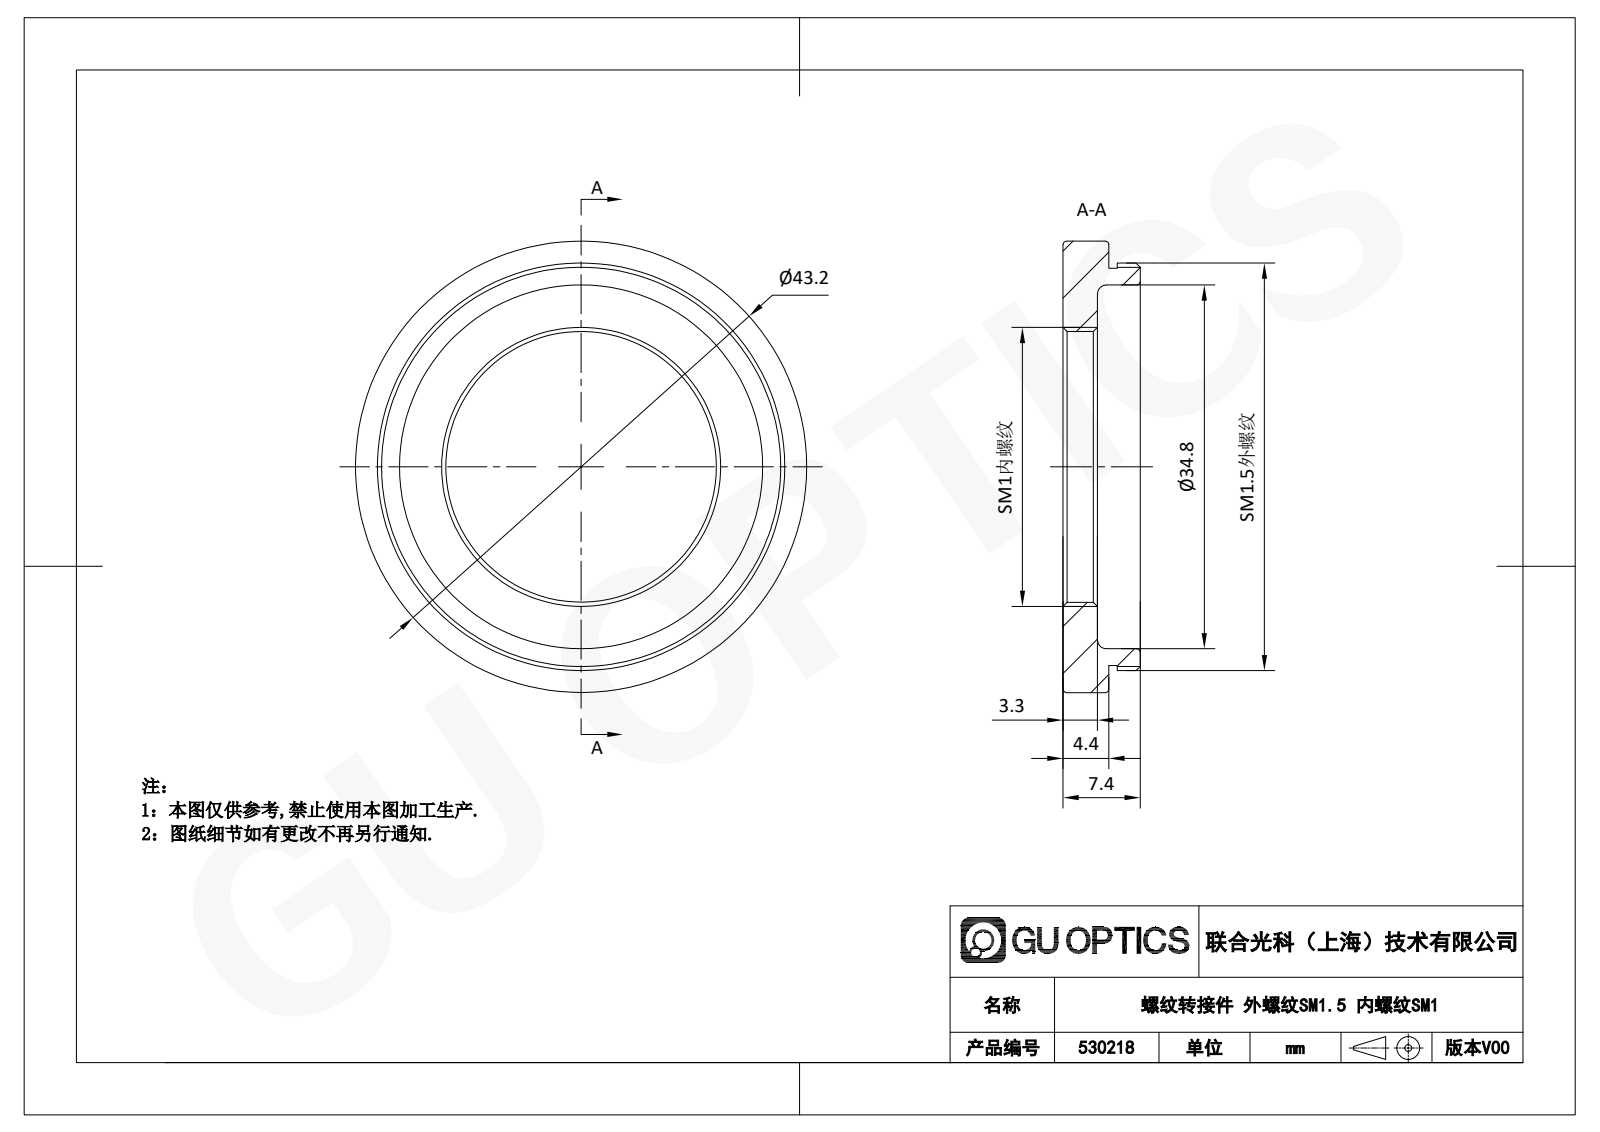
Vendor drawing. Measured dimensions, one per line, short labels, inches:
name: 530218
written by: SolidWorks 2020 (CONFIG_CONTROL_DESIGN)
unit: in
bodies: 1 solid, 17 faces (5 planar, 5 cylindrical, 7 other)
size: 1.701 × 1.701 × 0.291
volume: 0.264 in³; area: 5.461 in²
holes: 1× ⌀1.02, 1× ⌀1.37
bosses: 1× ⌀1.701, 1× ⌀1.535, 1× ⌀1.496
face distances: 0.13, 0.043, 0.173, 0.118, 0.161, 0.291, 0.087, 0.031, 0.075, 0.205
